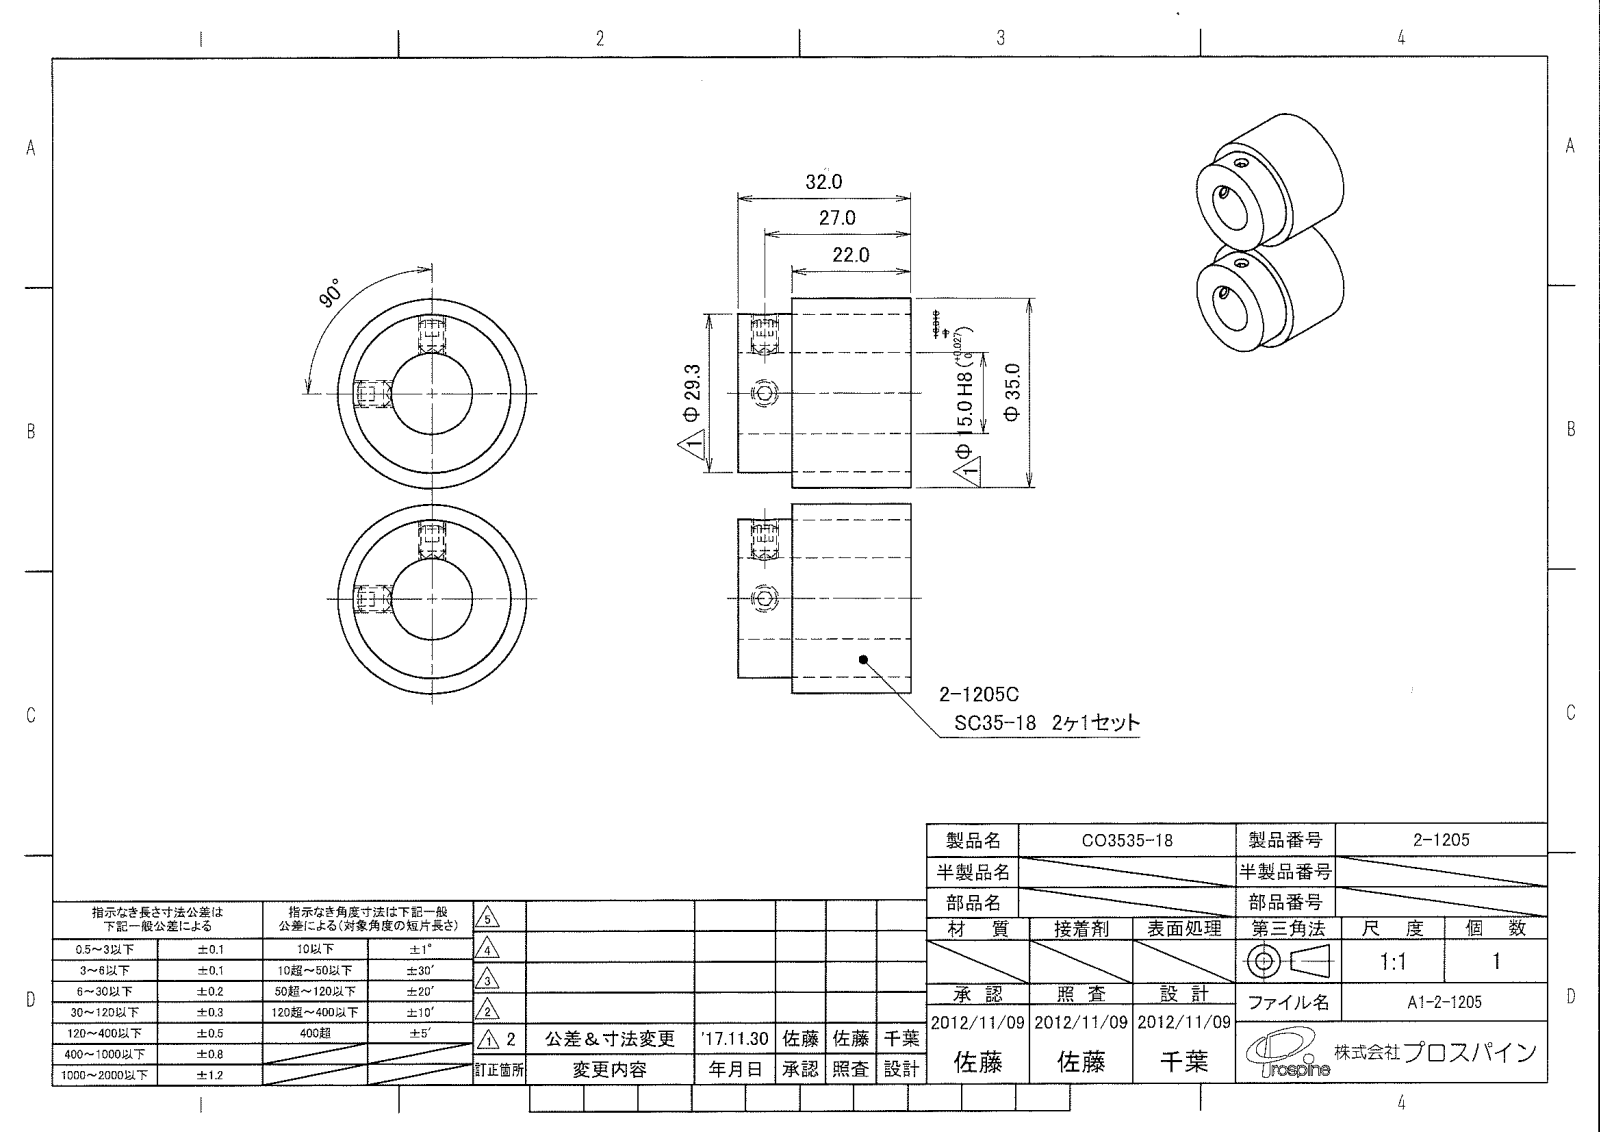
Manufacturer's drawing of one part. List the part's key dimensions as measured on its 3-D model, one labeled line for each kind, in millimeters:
STEP written by: PSStep 10.0 (CONFIG_CONTROL_DESIGN)
Units: millimetres
Bodies: 6 solids, 56 faces (33 planar, 11 cylindrical, 12 other)
Overall size (bounding box): 300 × 35 × 32
Volume: 22 395 mm³ · Surface area: 11 147 mm²
Round holes (diameter × count): ⌀4.2 ×2, ⌀15 ×1, ⌀29.1 ×1
Round bosses / shafts (diameter × count): ⌀5 ×2, ⌀35 ×1, ⌀29.3 ×1
Main face-to-face distances: 32, 10, 22, 2.5, 11.85, 9.46, 9.35, 11.96
